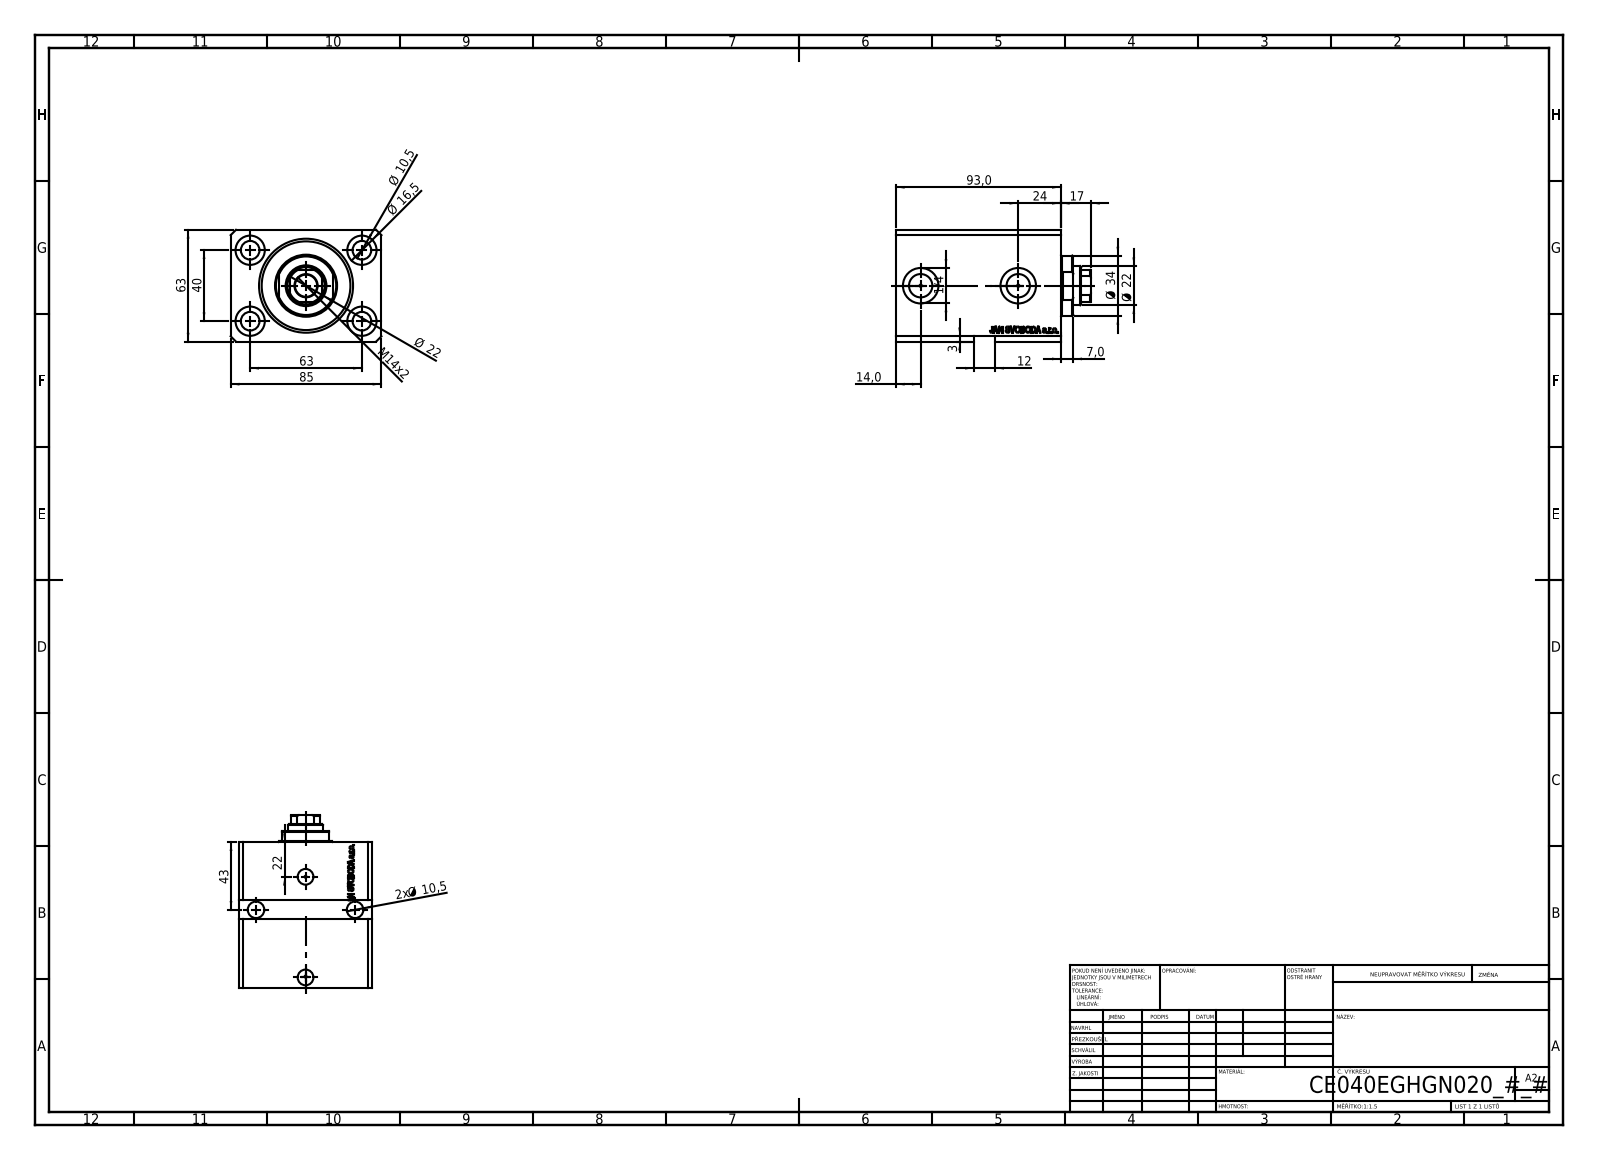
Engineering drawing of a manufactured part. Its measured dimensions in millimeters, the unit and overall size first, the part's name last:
Units: millimetres
Overall size (bounding box): 110 × 85 × 63
Round holes (diameter × count): ⌀10.5 ×6, ⌀1.25 ×4, ⌀16.5 ×4, ⌀10 ×2, ⌀13.16 ×2, ⌀20 ×2, ⌀12.5 ×1, ⌀22 ×1, ⌀40 ×1, ⌀53 ×1
Round bosses / shafts (diameter × count): ⌀34 ×1
Partial cylindrical surfaces — rounded edges, fillets, slot ends (radius × count): R10.5 ×1
Main face-to-face distances: 63, 85, 93, 17, 76, 11.4, 64.6, 81.6, 56, 44.6
Hole centre spacings: 37.31, 63, 37.86, 40, 52.88, 53.3, 74.63, 0.53
Volume: 427 173 mm³ · Surface area: 87 247 mm²
Bodies: 3 solids, 917 faces (459 planar, 84 cylindrical, 374 other)
Part name (STEP PRODUCT): V250CE_E_Body; V250CE_C_VCP; V250CE_VC_E
STEP written by: SolidWorks 2019 (CONFIG_CONTROL_DESIGN)
